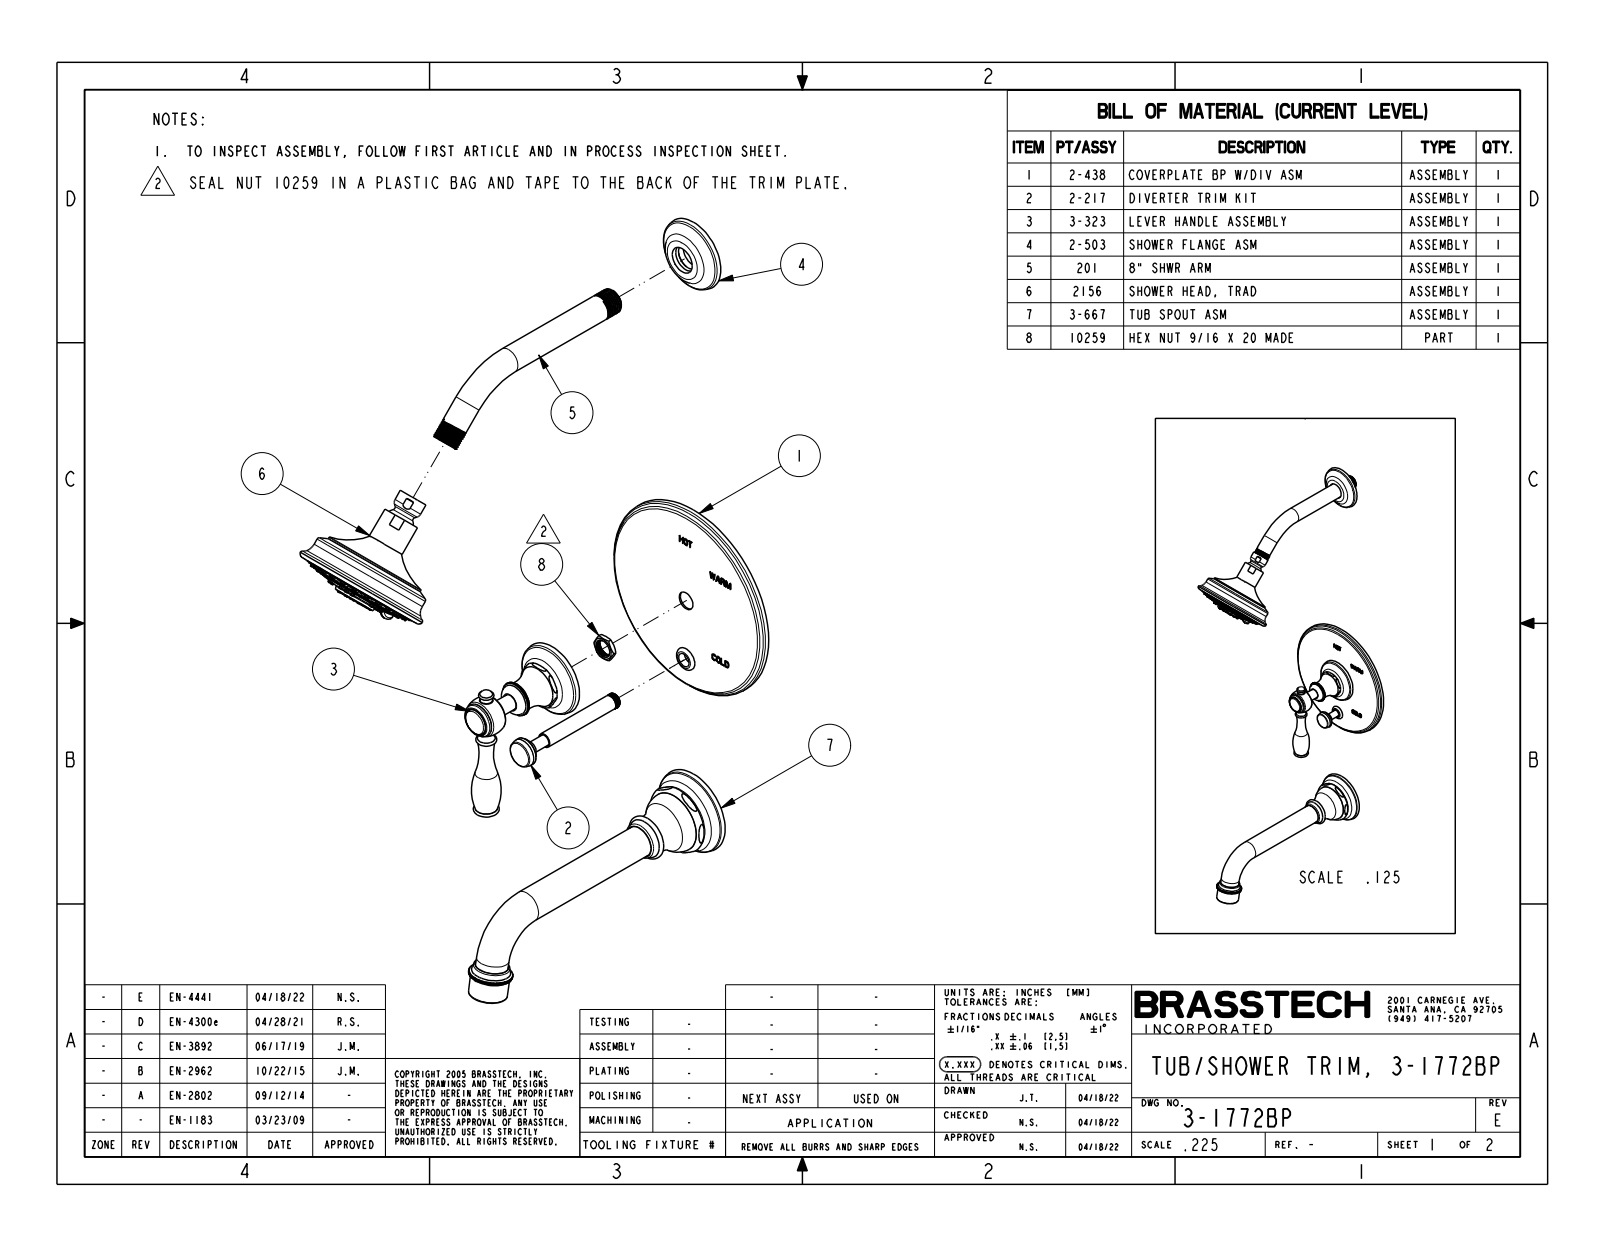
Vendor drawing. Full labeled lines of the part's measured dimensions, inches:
Part name (STEP PRODUCT): 3-1772BP
STEP written by: CREO PARAMETRIC BY PTC INC, 2018400 (CONFIG_CONTROL_DESIGN)
Units: inches
Bodies: 3 solids, 1784 faces (732 planar, 215 cylindrical, 837 other)
Overall size (bounding box): 24.56 × 10.05 × 6.5
Volume: 49 in³ · Surface area: 220.9 in²
Round holes (diameter × count): ⌀0.059 ×8, ⌀0.41 ×1, ⌀0.855 ×1, ⌀0.925 ×1
Round bosses / shafts (diameter × count): ⌀0.142 ×39, ⌀0.165 ×23, ⌀1 ×2, ⌀0.813 ×2, ⌀6.5 ×1, ⌀3.81 ×1, ⌀3.724 ×1, ⌀3.24 ×1
Partial cylindrical surfaces — rounded edges, fillets, slot ends (radius × count): R0.079 ×8, R0.02 ×2, R0.138 ×1, R0.472 ×1, R0.512 ×1, R0.63 ×1
Main face-to-face distances: 0.313, 0.48, 0.167, 0.063, 0.118, 0.181, 1.505, 1.192, 1.025, 2.853
Hole centre spacings: 0.443, 0.579, 0.818, 0.819, 1.069, 0.443, 0.578, 1.069
